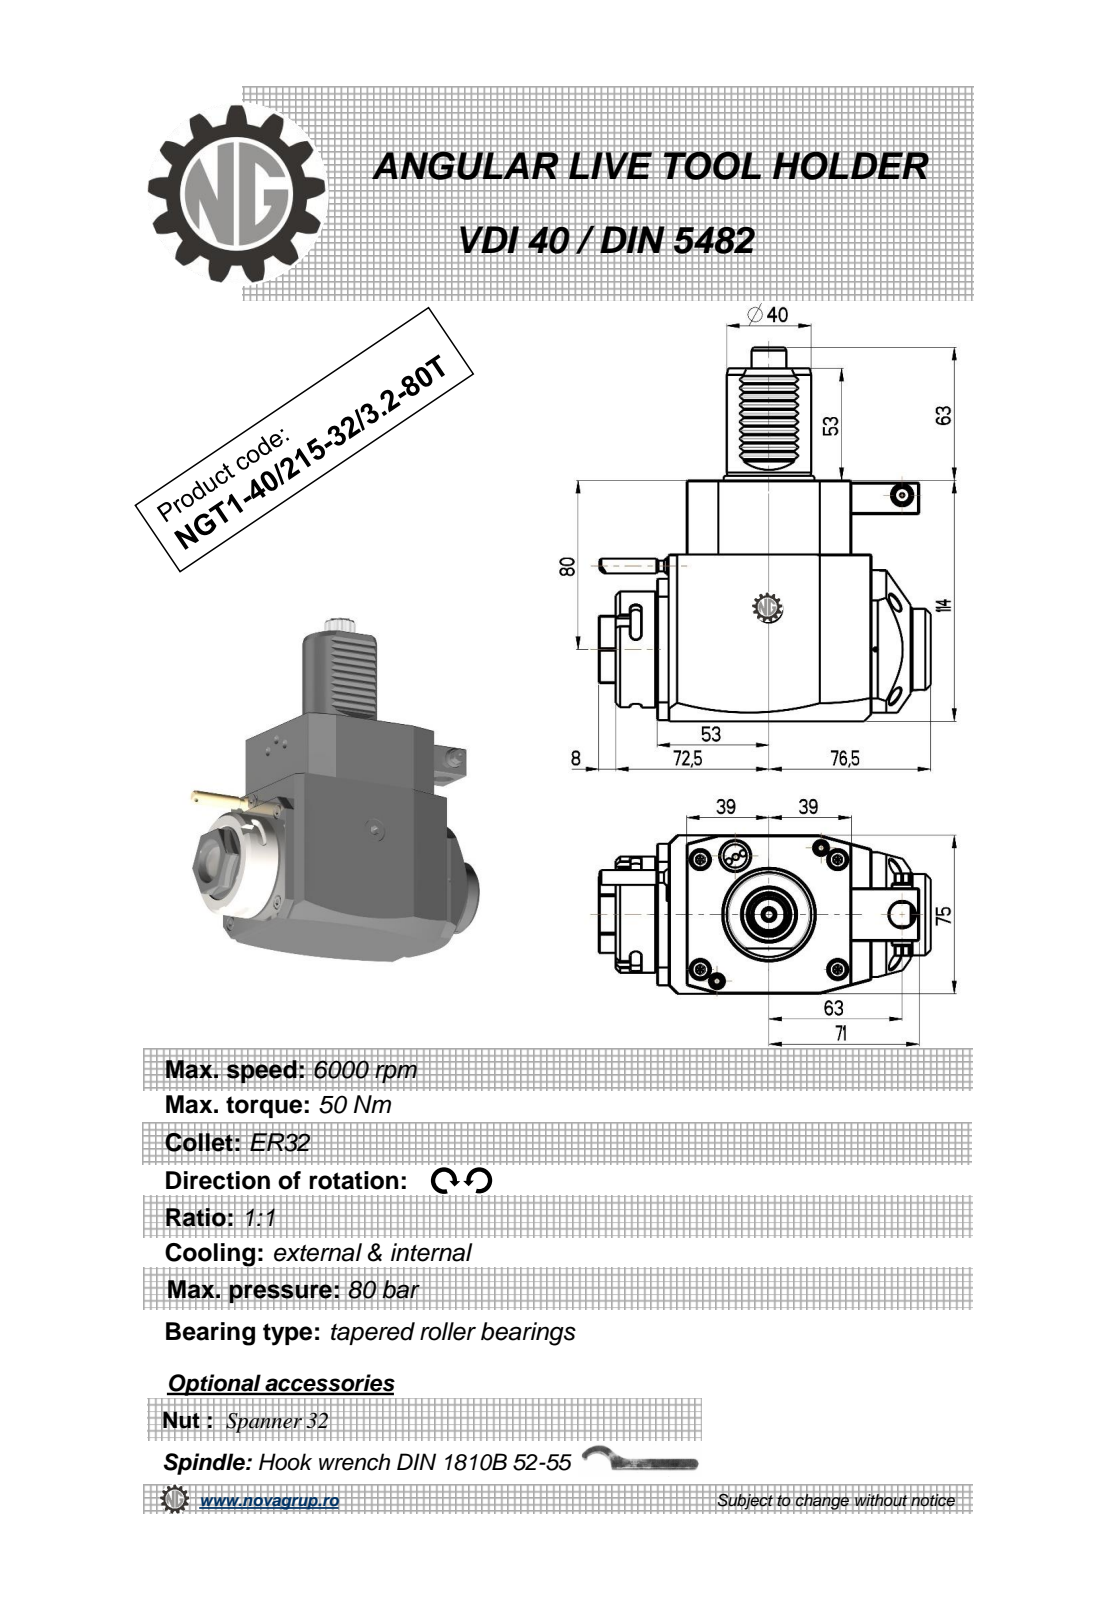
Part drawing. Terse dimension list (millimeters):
name: NGT1_40_215_32_3_2_80T
written by: PRO/ENGINEER BY PARAMETRIC TECHNOLOGY CORPORATION, 2010280 (CONFIG_CONTROL_DESIGN)
unit: mm
bodies: 1 solid, 394 faces (182 planar, 119 cylindrical, 93 other)
size: 177 × 157 × 75
volume: 963 761 mm³; area: 72 030 mm²
holes: 1× ⌀2, 1× ⌀2.5, 1× ⌀3, 1× ⌀4.2, 1× ⌀5.3, 1× ⌀9.5, 1× ⌀12, 1× ⌀23
bosses: 2× ⌀8, 1× ⌀55, 1× ⌀48, 1× ⌀40, 1× ⌀38.5, 1× ⌀10, 1× ⌀7, 1× ⌀5
rounds: 18× R3.03, 10× R0.3, 6× R2.5, 2× R180, 1× R0.5, 1× R3.85, 1× R4.25, 1× R6.75
face distances: 75, 114, 14, 92, 78, 25, 19.5, 33.5, 111.5, 35
hole spacings: 37.35, 43.2, 63, 72.5
